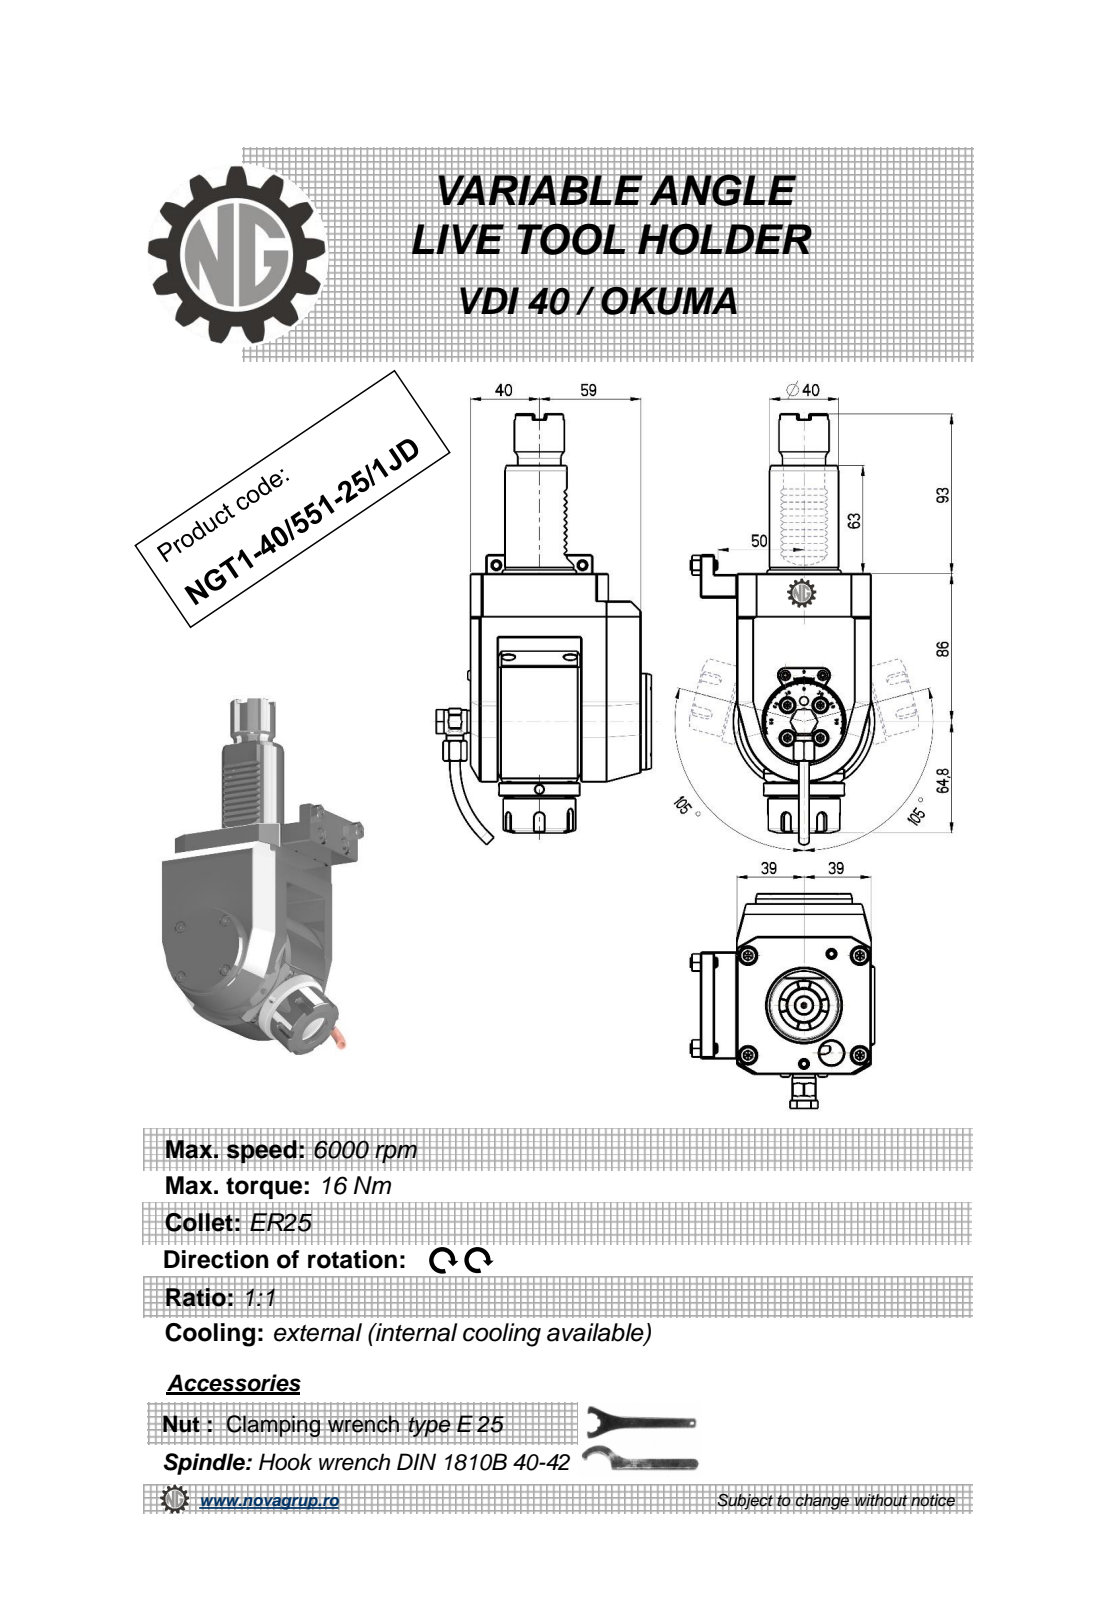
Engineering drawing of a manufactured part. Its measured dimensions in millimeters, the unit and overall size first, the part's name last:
Units: millimetres
Overall size (bounding box): 250.67 × 124.9 × 107
Round holes (diameter × count): ⌀4 ×3, ⌀5 ×2, ⌀3 ×1, ⌀6.2 ×1, ⌀9 ×1, ⌀10 ×1, ⌀11 ×1, ⌀20.3 ×1
Round bosses / shafts (diameter × count): ⌀6 ×4, ⌀5.7 ×2, ⌀82 ×1, ⌀56 ×1, ⌀47 ×1, ⌀42 ×1, ⌀40 ×1, ⌀35 ×1
Partial cylindrical surfaces — rounded edges, fillets, slot ends (radius × count): R0.3 ×10, R0.31 ×10, R3 ×5, R0.5 ×4, R10 ×3, R1 ×2, R7.7 ×1, R35 ×1
Main face-to-face distances: 99, 16, 37, 78, 21, 64, 6, 105, 48, 8
Hole centre spacings: 0.4, 39.45, 49, 49.4
Volume: 950 701 mm³ · Surface area: 88 416 mm²
Bodies: 1 solid, 601 faces (240 planar, 126 cylindrical, 235 other)
Part name (STEP PRODUCT): NGT1_40_551_25_1JD
STEP written by: PRO/ENGINEER BY PARAMETRIC TECHNOLOGY CORPORATION, 2010280 (CONFIG_CONTROL_DESIGN)
